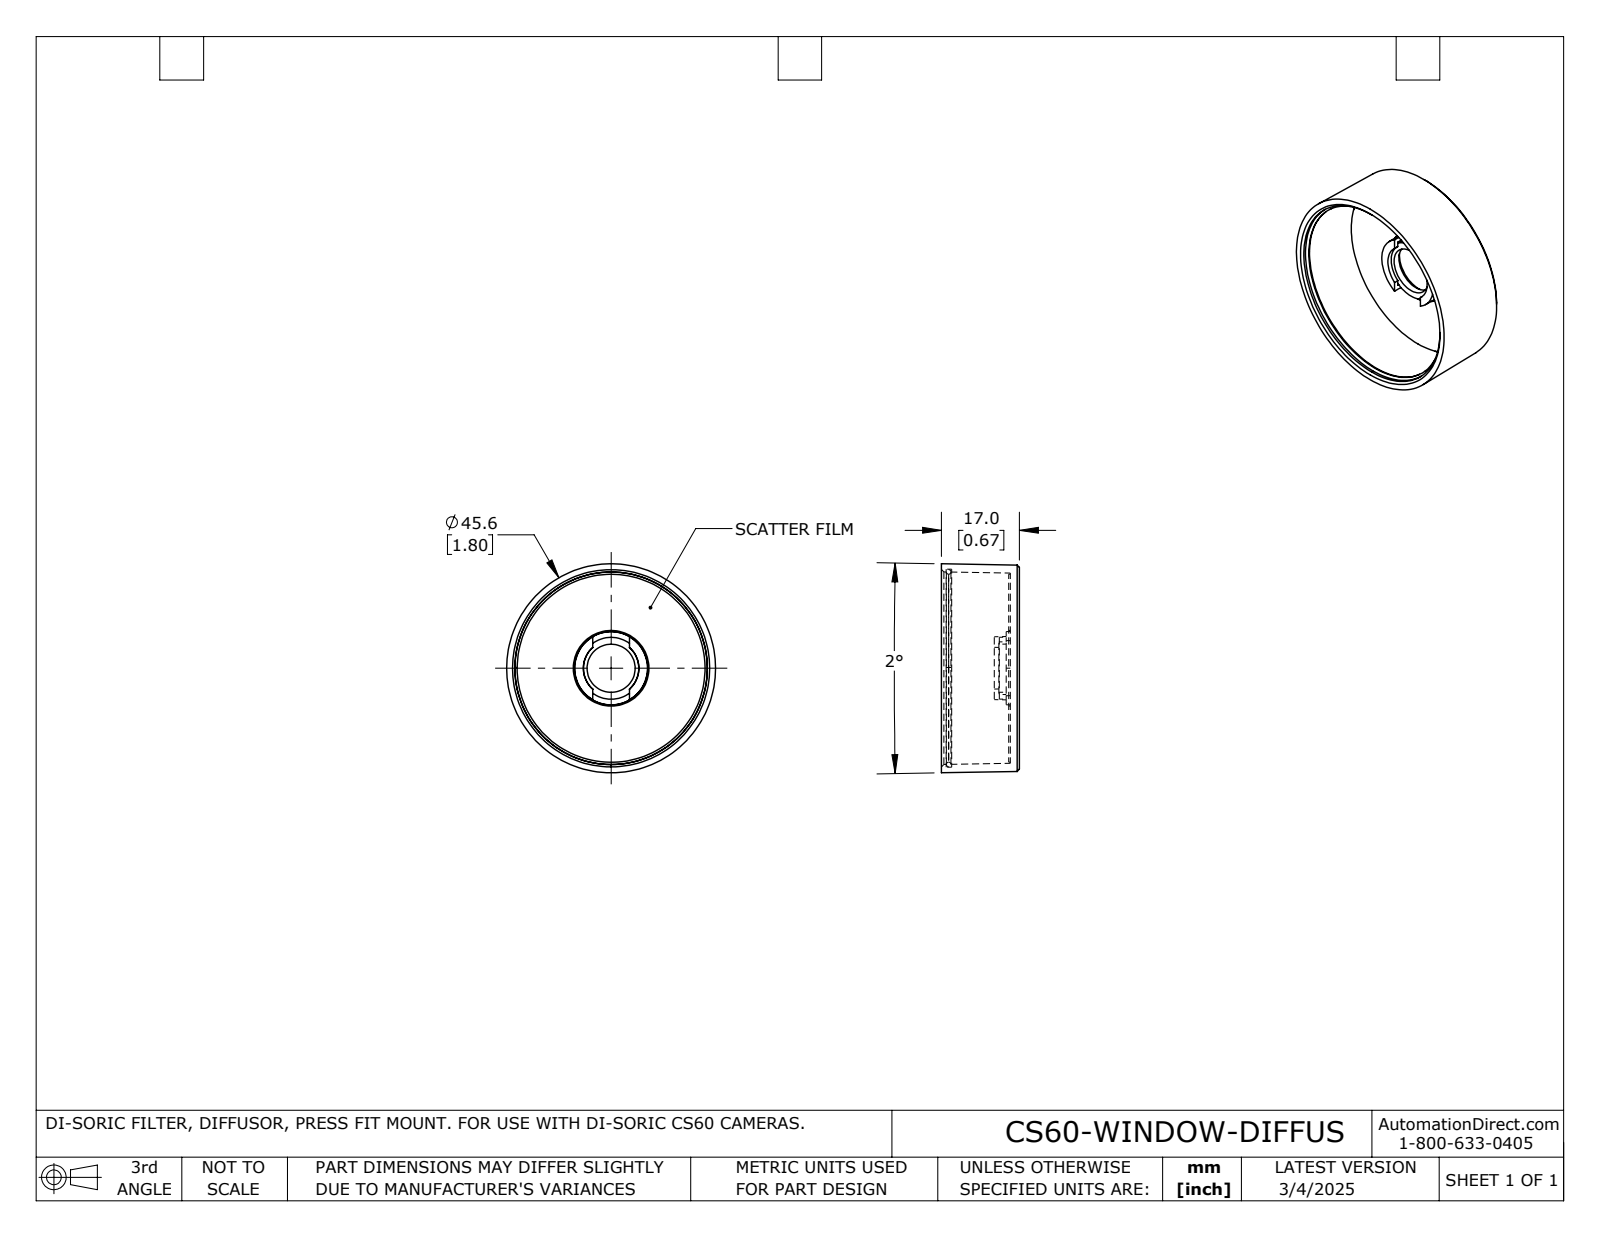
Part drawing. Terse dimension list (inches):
name: CS60-WINDOW-DIFFUS
written by: SolidWorks 2024 (AUTOMOTIVE_DESIGN)
unit: in
bodies: 4 solids, 36 faces (19 planar, 7 cylindrical, 10 other)
size: 1.795 × 1.795 × 0.669
volume: 0.456 in³; area: 16.85 in²
holes: 1× ⌀0.413, 1× ⌀0.65, 1× ⌀1.701
bosses: 1× ⌀1.614, 1× ⌀0.531
rounds: 1× R0.276
face distances: 0.079, 0.014, 0.093, 0.577, 0.591, 0.669, 0.555, 0.022, 0.035, 0.114
